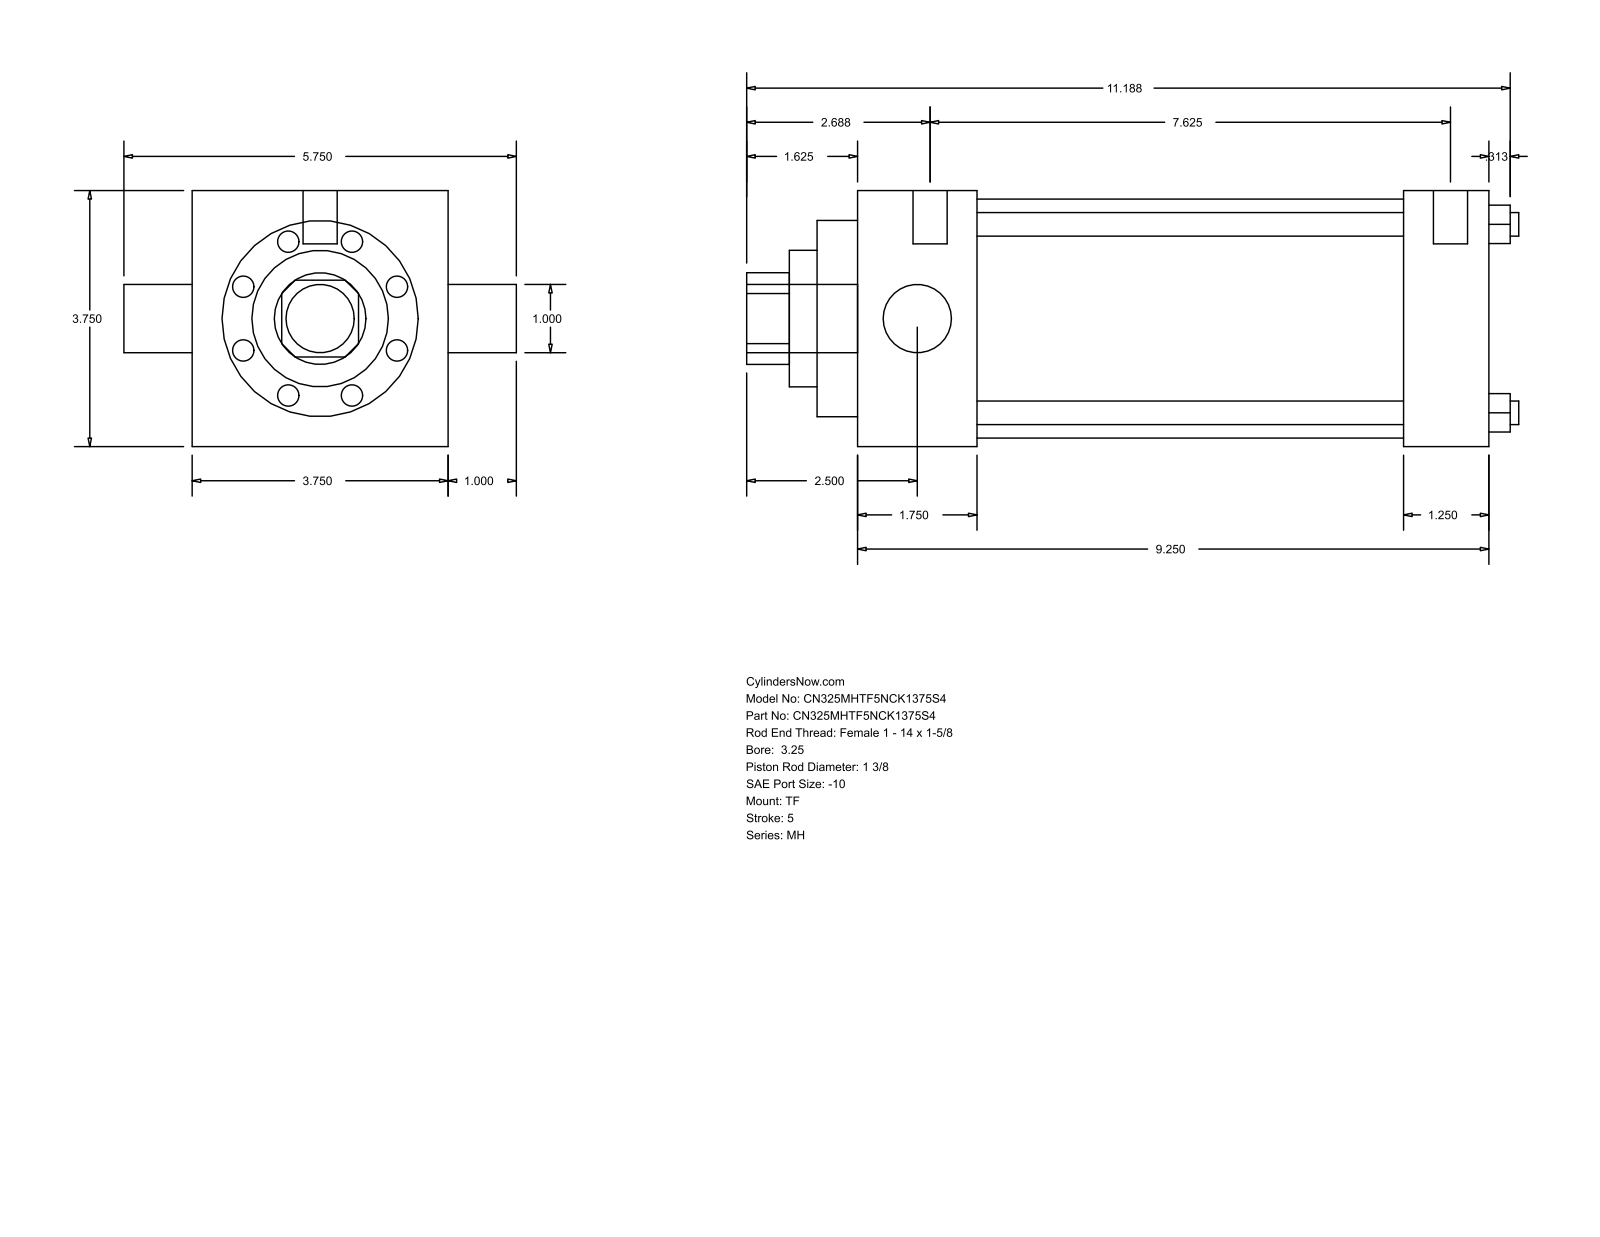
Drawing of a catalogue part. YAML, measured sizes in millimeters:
part_name: "MH_TF__0325_1.375"
step_written_by: "GSSL Pune (CONFIG_CONTROL_DESIGN)"
units: millimeters
bodies: {solids: 0, faces: 86, planar: 61, cylindrical: 25, other: 0}
overall_size: [287.34, 146.05, 95.25]
round_holes:
  - {diameter: 8.76, count: 4}
  - {diameter: 25.4, count: 1}
  - {diameter: 34.92, count: 1}
  - {diameter: 50.8, count: 1}
  - {diameter: 73.03, count: 1}
  - {diameter: 88.9, count: 1}
round_bosses_or_shafts:
  - {diameter: 5.56, count: 3}
  - {diameter: 12.7, count: 2}
  - {diameter: 25.4, count: 1}
partial_cylinders:
  - {radius: 17.06, count: 1}
face_to_face_distances: [95.24, 234.96, 44.45, 203.2, 158.75, 190.51, 31.76, 15.08, 59.53, 218.28]
hole_center_spacings: [49.57, 70.1, 99.14]
